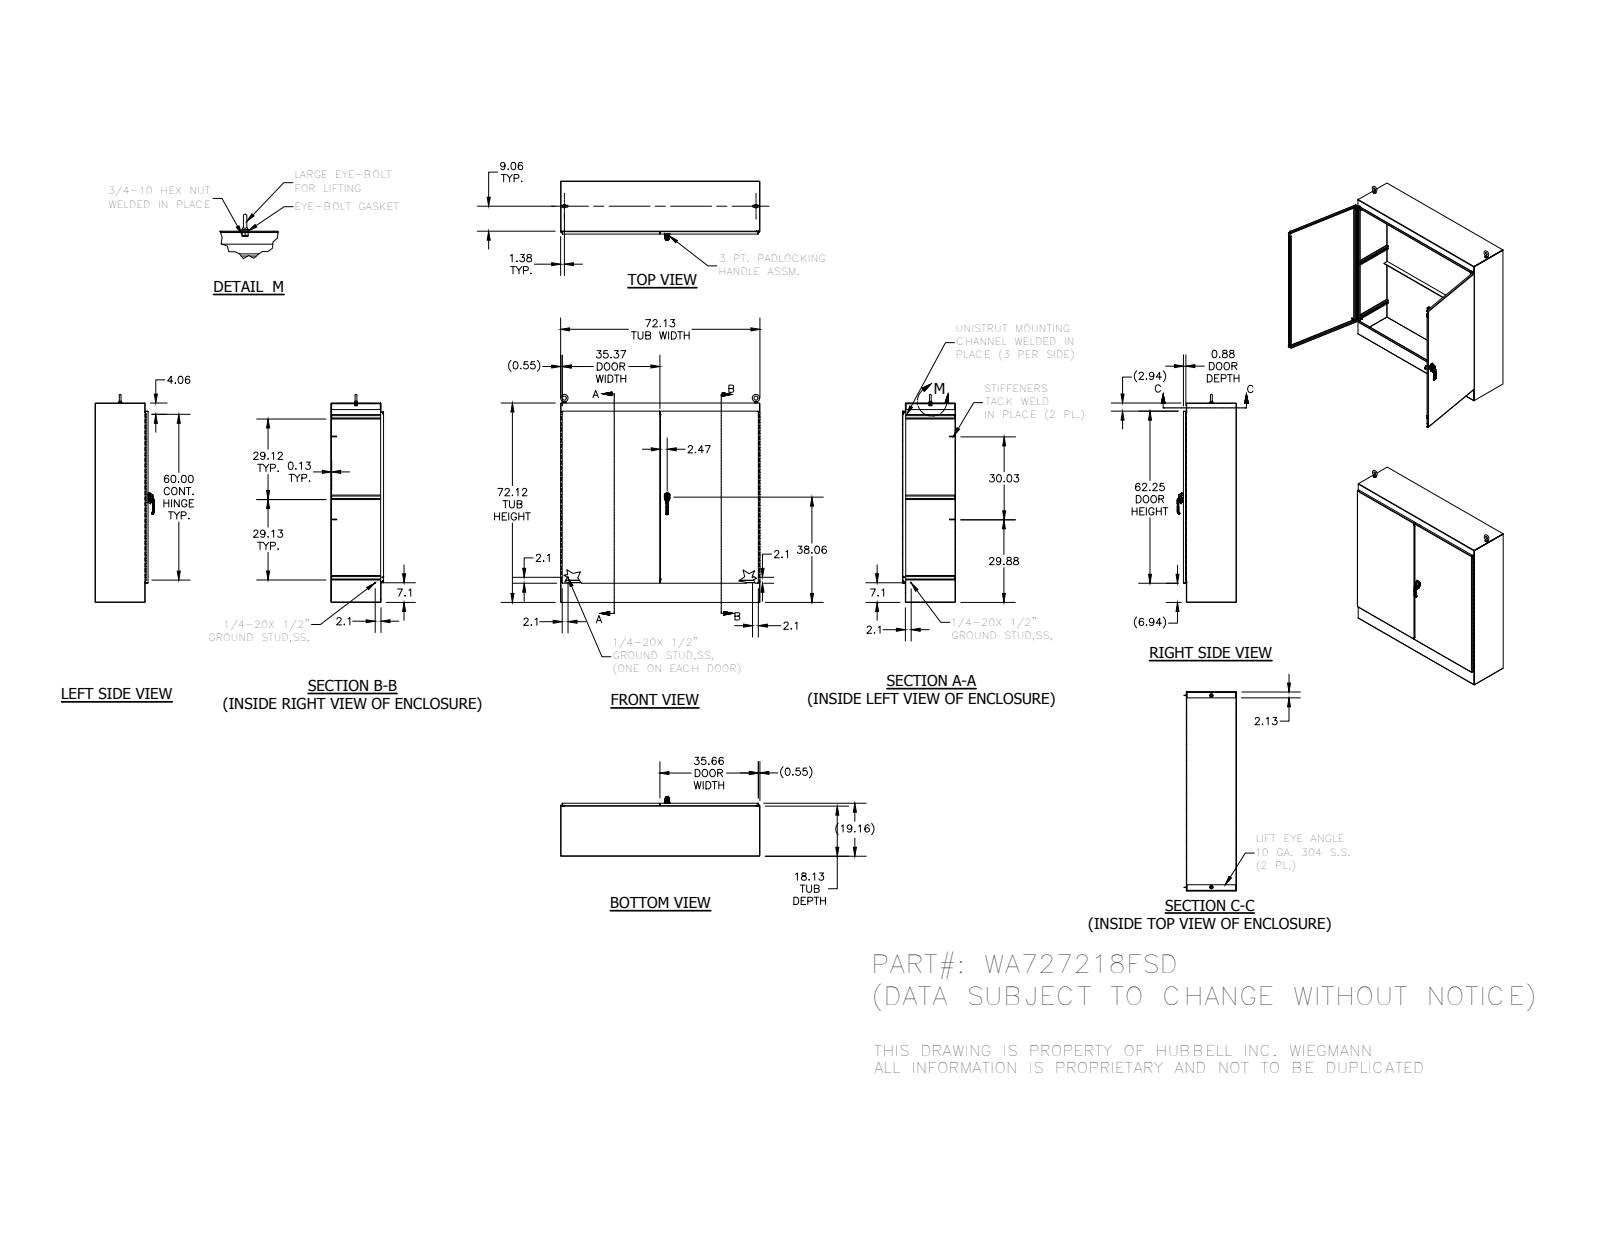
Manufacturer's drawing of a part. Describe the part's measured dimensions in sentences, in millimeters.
The part is named "FUN00101; HFW3025; 316298; 349132 (+8 more)". Its 3-D file was written by "Autodesk Inventor 2014 (AUTOMOTIVE_DESIGN)". It is 66 solids with 3780 faces: 1777 planar, 1263 cylindrical and 740 other. Overall it measures 1911.29 by 1832.34 by 544.36 millimeters. Its volume is 37 200 000 cubic millimeters and its surface area 23 360 000 square millimeters. Round holes: 8 of diameter 7.02, 4 of diameter 5.08, 3 of diameter 5.4, 3 of diameter 6, 3 of diameter 7.11, 2 of diameter 3.17, 2 of diameter 6.13, 2 of diameter 6.35, 2 of diameter 6.41, 2 of diameter 10.16, 2 of diameter 10.33, 2 of diameter 10.5. Round bosses or shafts: 5 of diameter 6.35, 3 of diameter 8.56, 2 of diameter 31.75, 2 of diameter 28.45, 2 of diameter 25.4, 2 of diameter 19.05, 2 of diameter 14.29, 2 of diameter 13.37. Partial cylindrical surfaces (rounded edges, fillets, slot ends): 164 of radius 0.5, 84 of radius 0.3, 24 of radius 0.79, 21 of radius 3.97, 19 of radius 0.47, 16 of radius 0.25, 15 of radius 2, 14 of radius 1.27. The main face-to-face distances are 3.18, 1828.8, 3.17, 483.57, 480.39, 486.74, 483.56, 1825.62, 1831.98, 457.2. The hole center spacings are 6, 6.5, 9.67, 9.69, 9.72, 12.49, 12.5, 19.36.
